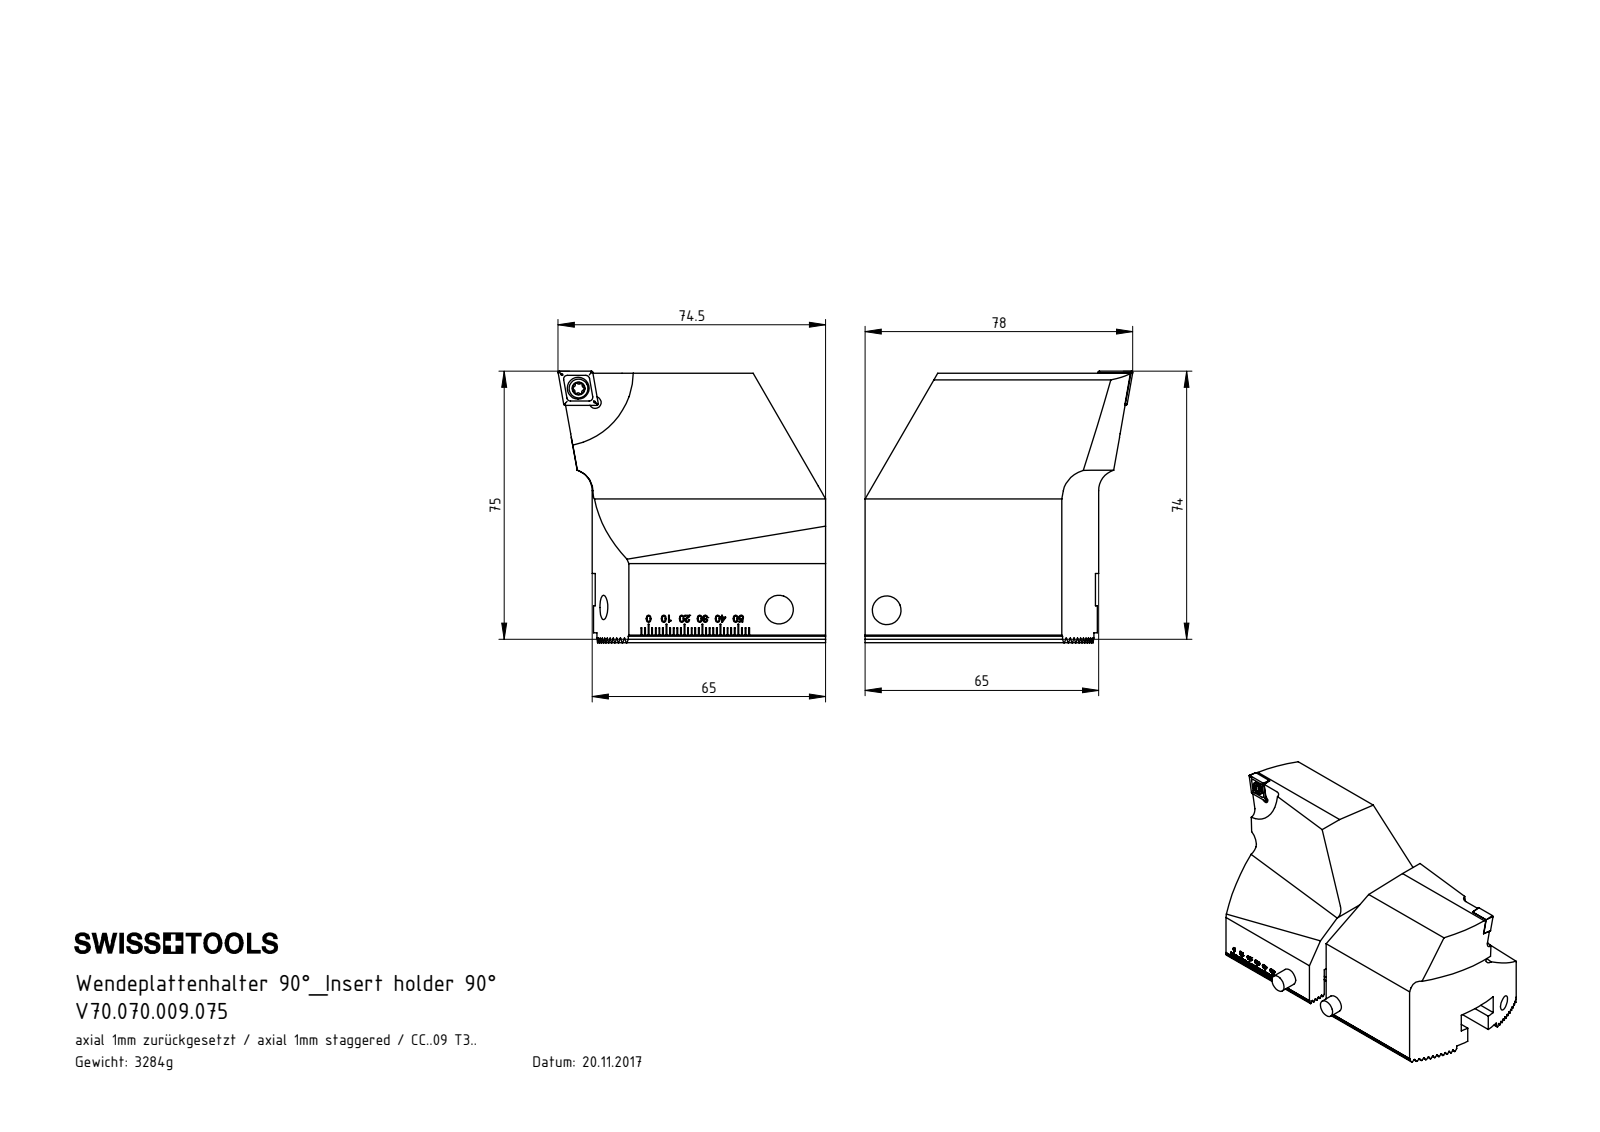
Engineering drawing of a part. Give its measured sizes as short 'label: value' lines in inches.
name: ISO 4028 - M8 x 35; ISO 8734 - 8 x 20 m6; CCMT09T304; VK1-WCB.001.075_A (+2 more)
written by: SolidWorks 2017 (AUTOMOTIVE_DESIGN)
unit: in
bodies: 6 solids, 525 faces (343 planar, 52 cylindrical, 130 other)
size: 3.701 × 2.975 × 2.933
volume: 12.79 in³; area: 49.85 in²
holes: 2× ⌀0.13, 2× ⌀0.315, 1× ⌀0.173, 1× ⌀0.24, 1× ⌀0.268
bosses: 1× ⌀0.315, 1× ⌀0.217, 1× ⌀0.207, 1× ⌀0.157
rounds: 22× R0.006, 6× R0.013, 6× R0.023, 1× R0.157, 1× R0.207, 1× R0.827, 1× R2.559, 1× R2.717
face distances: 0.068, 0.341, 0.136, 0.273, 1.705, 0.409, 1.637, 0.965, 1.791, 0.205
hole spacings: 0.239, 0.244, 0.276, 3.034, 3.229, 3.27, 3.275, 3.467
